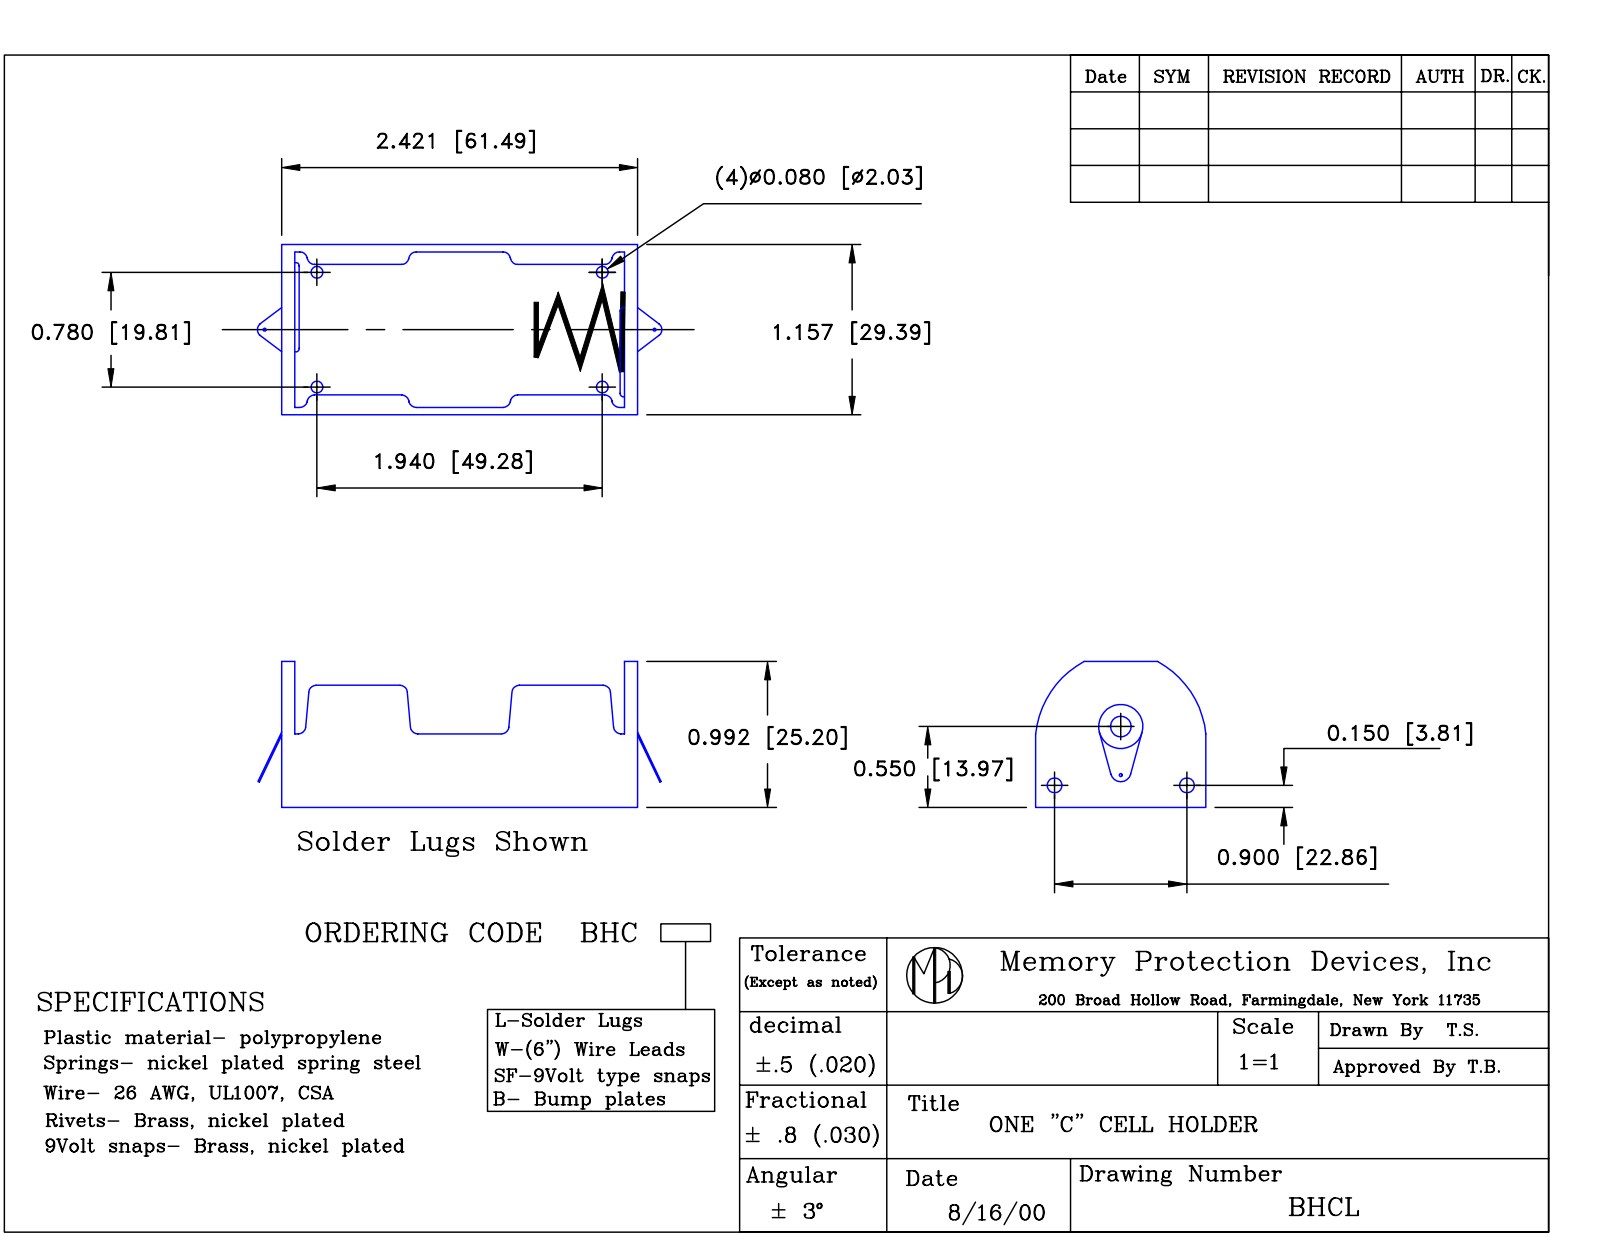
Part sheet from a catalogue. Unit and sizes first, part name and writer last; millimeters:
Units: millimetres
Overall size (bounding box): 64.8 × 29.39 × 25.2
Round holes (diameter × count): ⌀2.03 ×4, ⌀0.9 ×2, ⌀2.5 ×2, ⌀4.2 ×2, ⌀2.2 ×1, ⌀3 ×1, ⌀7.7 ×1
Round bosses / shafts (diameter × count): ⌀5 ×2, ⌀4.5 ×1, ⌀4 ×1, ⌀0.7 ×1
Partial cylindrical surfaces — rounded edges, fillets, slot ends (radius × count): R1.3 ×12, R1 ×4, R3 ×3, R1.6 ×2, R4 ×2, R4.21 ×2, R19.5 ×2, R20.6 ×2
Main face-to-face distances: 1.1, 60.1, 1.11, 28.29, 61.2, 59, 29.4, 27.18, 0.31, 60.89
Hole centre spacings: 49.5, 9.91, 14.82, 49, 52.85, 9.92, 19.8, 19.81
Volume: 5 887 mm³ · Surface area: 11 557 mm²
Bodies: 3 solids, 192 faces (77 planar, 93 cylindrical, 22 other)
Part name (STEP PRODUCT): BHCL
STEP written by: SolidWorks 2017 (AUTOMOTIVE_DESIGN)
